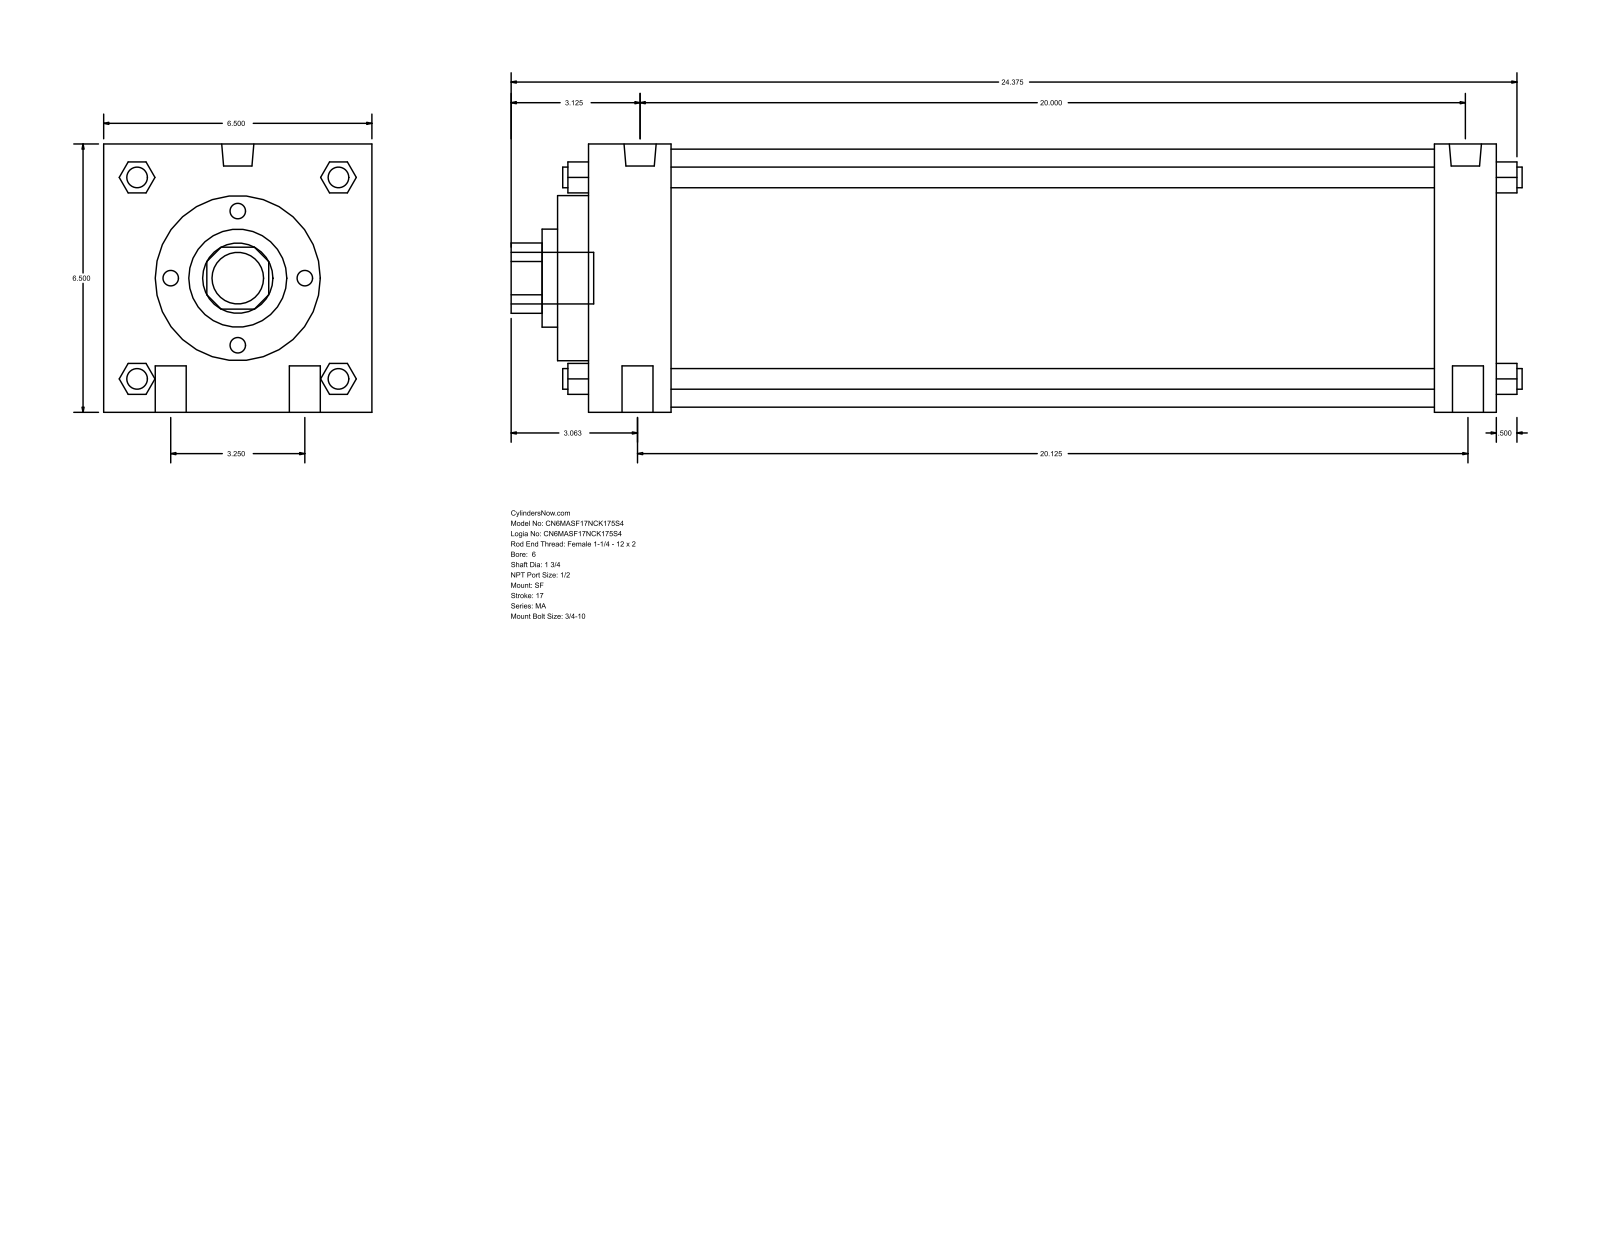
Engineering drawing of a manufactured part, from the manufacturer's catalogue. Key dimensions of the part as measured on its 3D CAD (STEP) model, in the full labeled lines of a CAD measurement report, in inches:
Part name (STEP PRODUCT): MA_SF__0600_1.75
STEP written by: GSSL Pune (CONFIG_CONTROL_DESIGN)
Units: inches
Bodies: 0 solids, 126 faces (95 planar, 31 cylindrical, 0 other)
Overall size (bounding box): 24.5 × 6.5 × 6.5
Round holes (diameter × count): ⌀1.75 ×1, ⌀2.375 ×1, ⌀4 ×1, ⌀6.25 ×1
Round bosses / shafts (diameter × count): ⌀0.75 ×4, ⌀0.5 ×4, ⌀0.778 ×2, ⌀0.687 ×2, ⌀1.25 ×1
Partial cylindrical surfaces — rounded edges, fillets, slot ends (radius × count): R0.852 ×1
Main face-to-face distances: 6.5, 22, 0.75, 2, 20.5, 1.5, 18.5, 20, 2.75, 21.25
